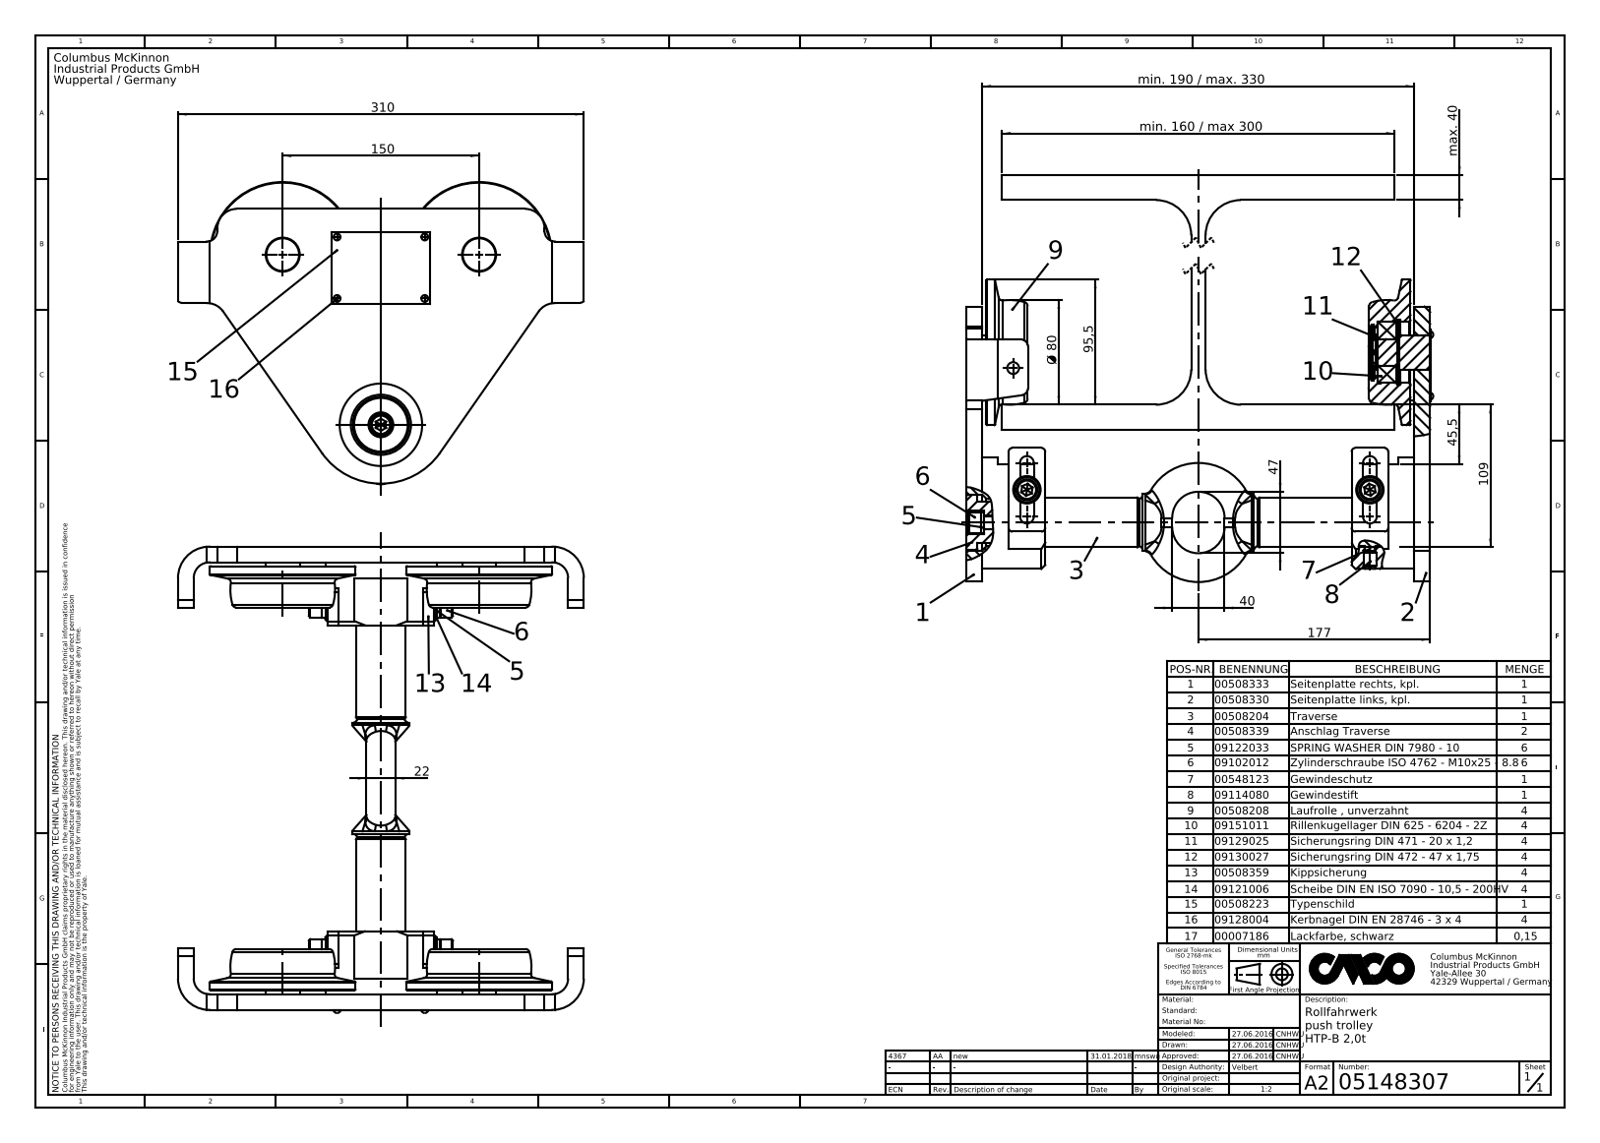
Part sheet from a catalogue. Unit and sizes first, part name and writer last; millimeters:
Units: millimetres
Overall size (bounding box): 416.5 × 400 × 356.4
Round holes (diameter × count): ⌀2 ×6, ⌀2.5 ×6, ⌀3 ×4, ⌀3.5 ×4, ⌀8.5 ×4, ⌀10.2 ×3, ⌀9 ×2, ⌀10.5 ×2, ⌀19 ×2, ⌀26 ×2, ⌀36.71 ×2, ⌀38 ×2
Round bosses / shafts (diameter × count): ⌀10 ×4, ⌀5.2 ×4, ⌀16 ×3, ⌀111 ×2, ⌀49.5 ×2, ⌀26.99 ×2, ⌀21 ×2, ⌀20 ×2
Partial cylindrical surfaces — rounded edges, fillets, slot ends (radius × count): R3 ×8, R2.5 ×6, R2 ×4, R5.25 ×4, R6 ×4, R12 ×4, R15 ×4, R24 ×4
Main face-to-face distances: 19, 281, 300, 12, 262, 11, 159.5, 171.5, 182.5, 342
Hole centre spacings: 10.13, 11.57, 21.55, 150, 11.49, 6.25, 116.93, 5
Volume: 8 518 000 mm³ · Surface area: 1 250 000 mm²
Bodies: 55 solids, 1170 faces (398 planar, 442 cylindrical, 330 other)
Part name (STEP PRODUCT): HTP-B 2,0t
STEP written by: SolidWorks 2015 (AUTOMOTIVE_DESIGN)
